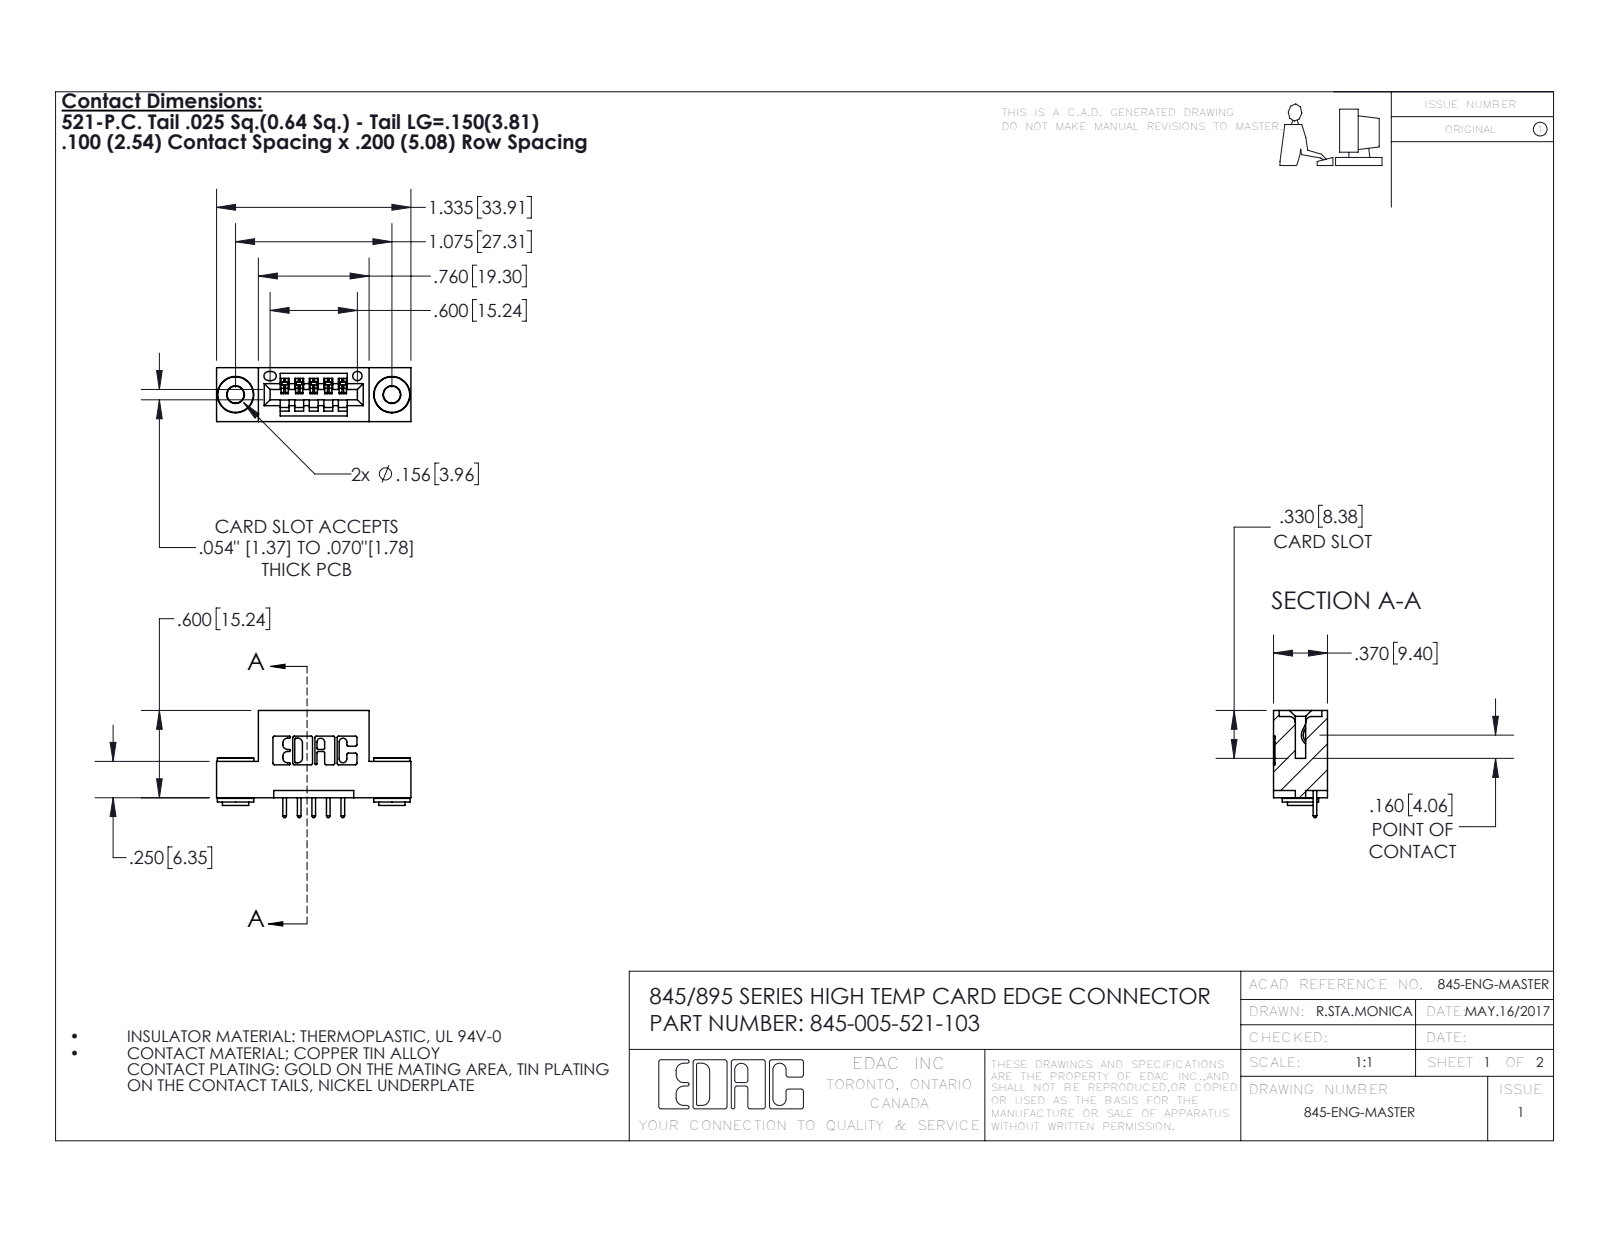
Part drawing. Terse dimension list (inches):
name: 345-250-002_345-250-002-102; 345-005-521-103; 345 Part_Flush Mounting Lugs - 0.156 Dia-TH; 345-292-001_345-293-121
written by: SolidWorks 2016 (CONFIG_CONTROL_DESIGN)
unit: in
bodies: 8 solids, 454 faces (290 planar, 156 cylindrical, 8 other)
size: 1.335 × 0.737 × 0.37
volume: 0.178 in³; area: 5.487 in²
holes: 2× ⌀0.116, 2× ⌀0.156, 1× ⌀0.064
bosses: 2× ⌀0.25, 2× ⌀0.18, 2× ⌀0.136
rounds: 22× R0.01, 10× R0.006, 10× R0.01, 6× R0.007, 6× R0.031, 3× R0.026, 2× R0.031, 2× R0.04
face distances: 0.2, 0.37, 0.072, 0.298, 0.1, 0.25, 0.025, 0.35, 0.098, 0.272
hole spacings: 0.27, 0.847, 1.075
